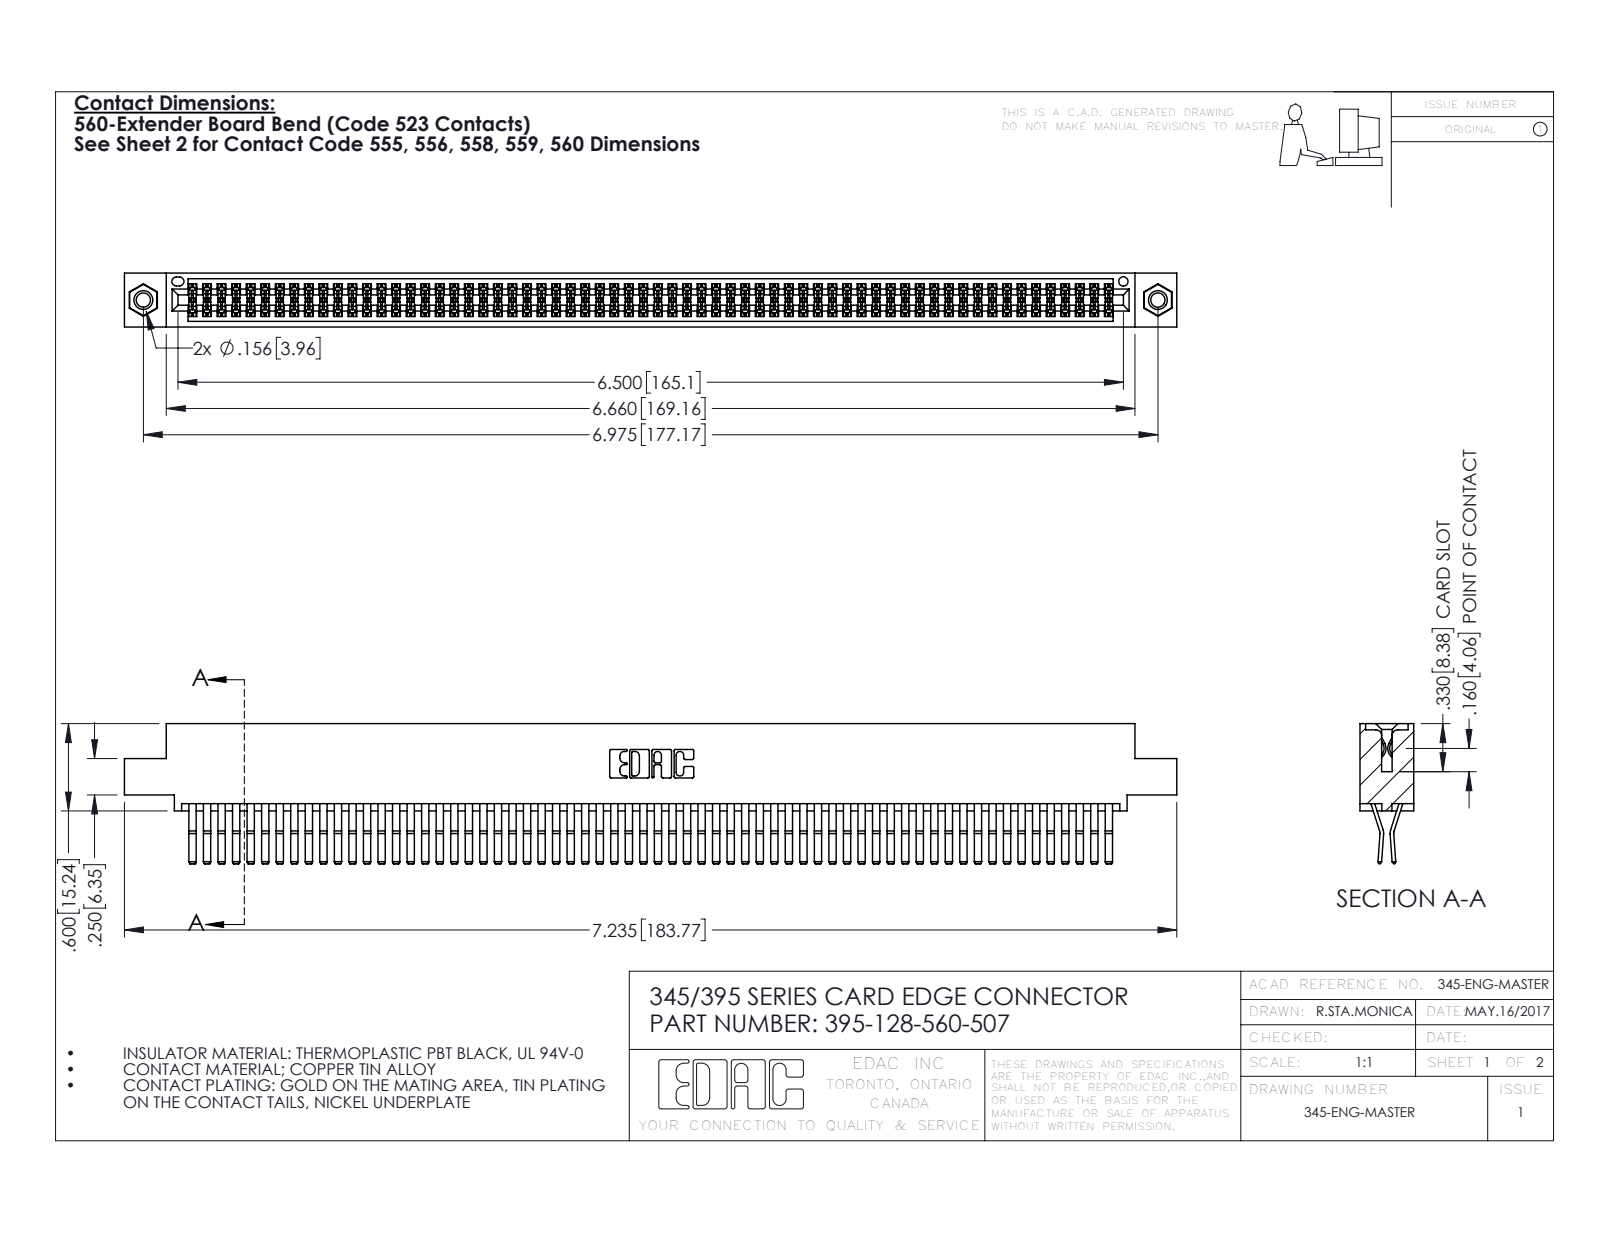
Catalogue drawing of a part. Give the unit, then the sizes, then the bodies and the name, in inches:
Units: inches
Overall size (bounding box): 7.235 × 0.962 × 0.37
Round holes (diameter × count): ⌀0.098 ×2, ⌀0.125 ×2, ⌀0.156 ×2, ⌀0.064 ×1
Round bosses / shafts (diameter × count): ⌀0.155 ×2
Partial cylindrical surfaces — rounded edges, fillets, slot ends (radius × count): R0.006 ×192, R0.01 ×22, R0.007 ×6, R0.031 ×6, R0.026 ×3, R0.01 ×2, R0.014 ×2, R0.019 ×2
Main face-to-face distances: 0.025, 0.072, 0.298, 0.37, 0.2, 0.098, 0.272, 0.225, 0.175, 0.149
Hole centre spacings: 0.27, 6.739, 6.975
Volume: 1.148 in³ · Surface area: 47.28 in²
Bodies: 131 solids, 6846 faces (4340 planar, 2490 cylindrical, 16 other)
Part name (STEP PRODUCT): 345-292-001_560 Tail; 395-128-560-507; 345 Part_0.110 Offset - 0.156 Dia-TI; 345-250-001_345-250-005-103
STEP written by: SolidWorks 2016 (CONFIG_CONTROL_DESIGN)
